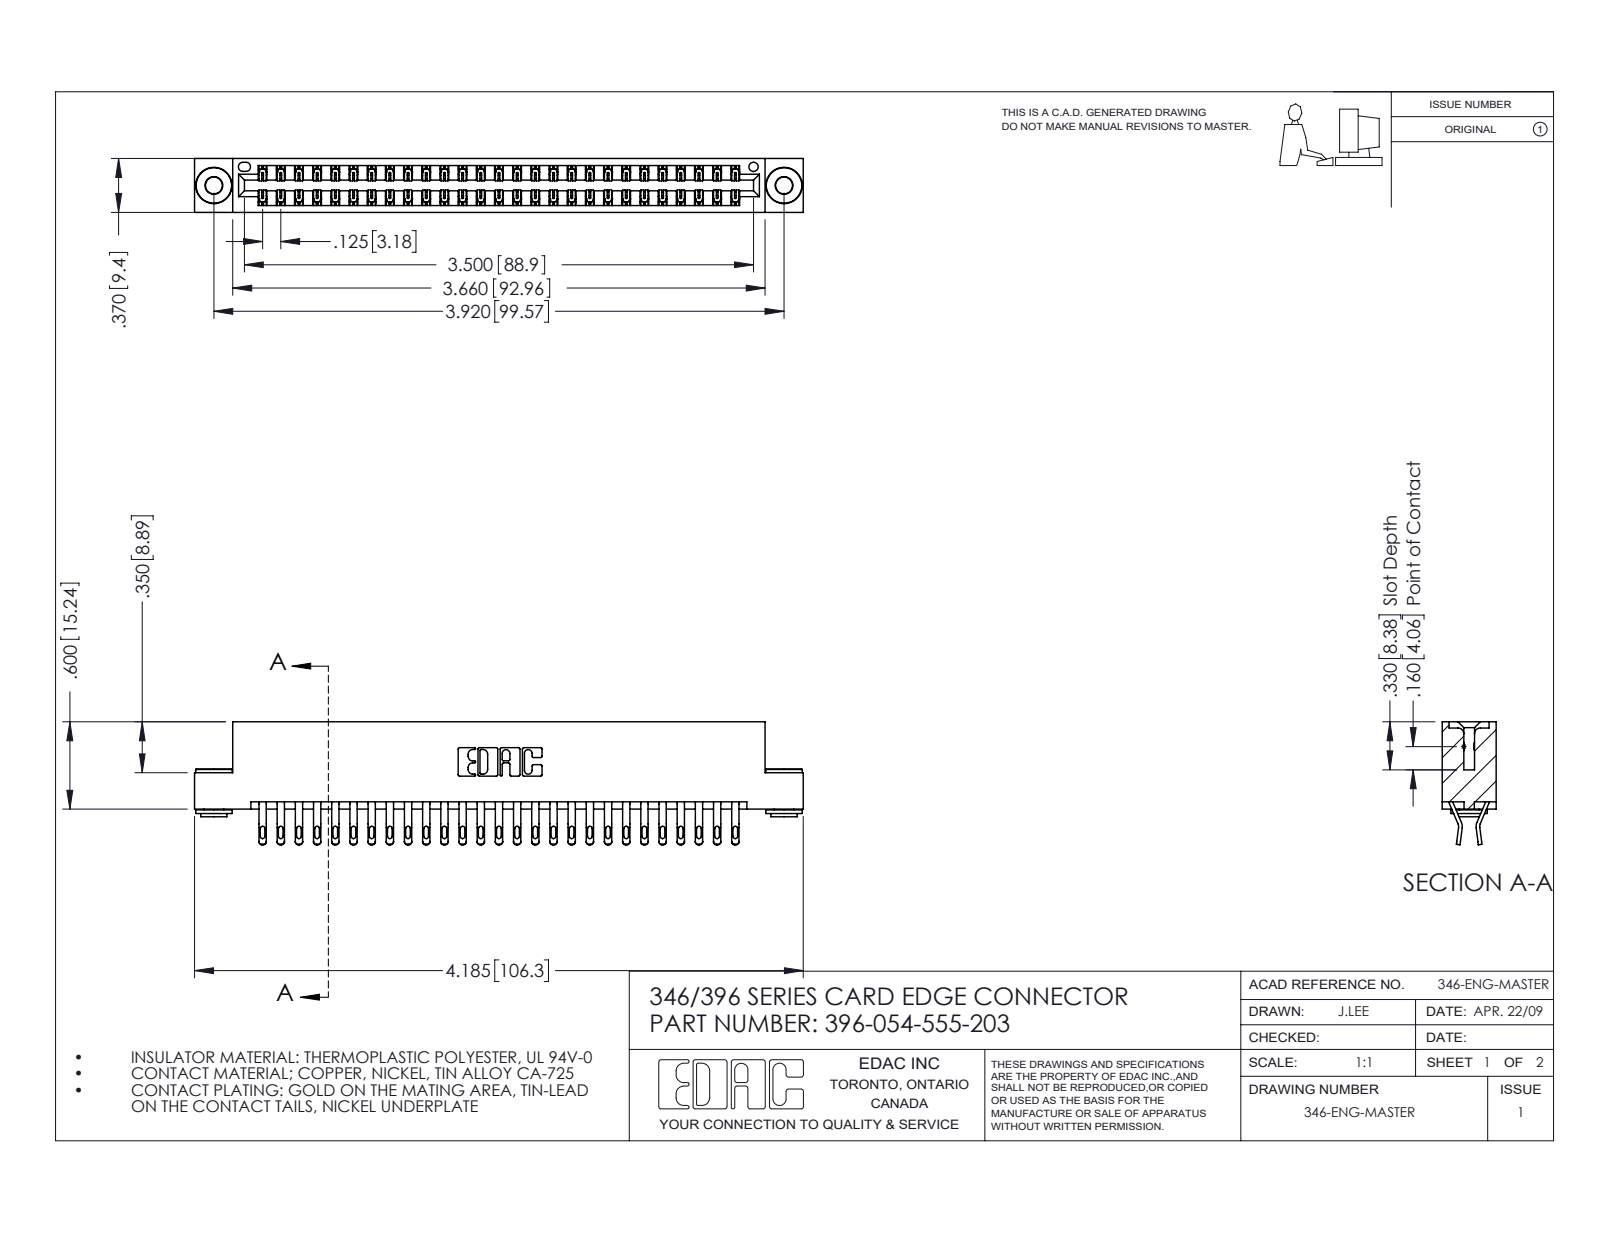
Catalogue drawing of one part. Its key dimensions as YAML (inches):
part_name: "396-054-555-203; 345-292-001_555 Tail; 346 Part_Flush Mounting Lugs - 0.156 Dia-TH; 345-250-002_345-250-002-102"
step_written_by: "SolidWorks 2016 (CONFIG_CONTROL_DESIGN)"
units: inches
bodies: {solids: 57, faces: 3292, planar: 1868, cylindrical: 1416, other: 8}
overall_size: [4.185, 0.845, 0.37]
volume: 0.636
surface_area: 23.04
round_holes:
  - {diameter: 0.116, count: 2}
  - {diameter: 0.156, count: 2}
  - {diameter: 0.064, count: 1}
round_bosses_or_shafts:
  - {diameter: 0.25, count: 2}
  - {diameter: 0.18, count: 2}
  - {diameter: 0.136, count: 2}
partial_cylinders:
  - {radius: 0.016, count: 108}
  - {radius: 0.02, count: 108}
  - {radius: 0.006, count: 81}
  - {radius: 0.01, count: 22}
  - {radius: 0.007, count: 6}
  - {radius: 0.031, count: 6}
  - {radius: 0.026, count: 3}
  - {radius: 0.01, count: 2}
face_to_face_distances: [0.048, 0.322, 0.25, 0.37, 0.025, 0.072, 0.298, 0.275, 0.148, 0.222]
hole_center_spacings: [0.246, 3.712, 3.92]
